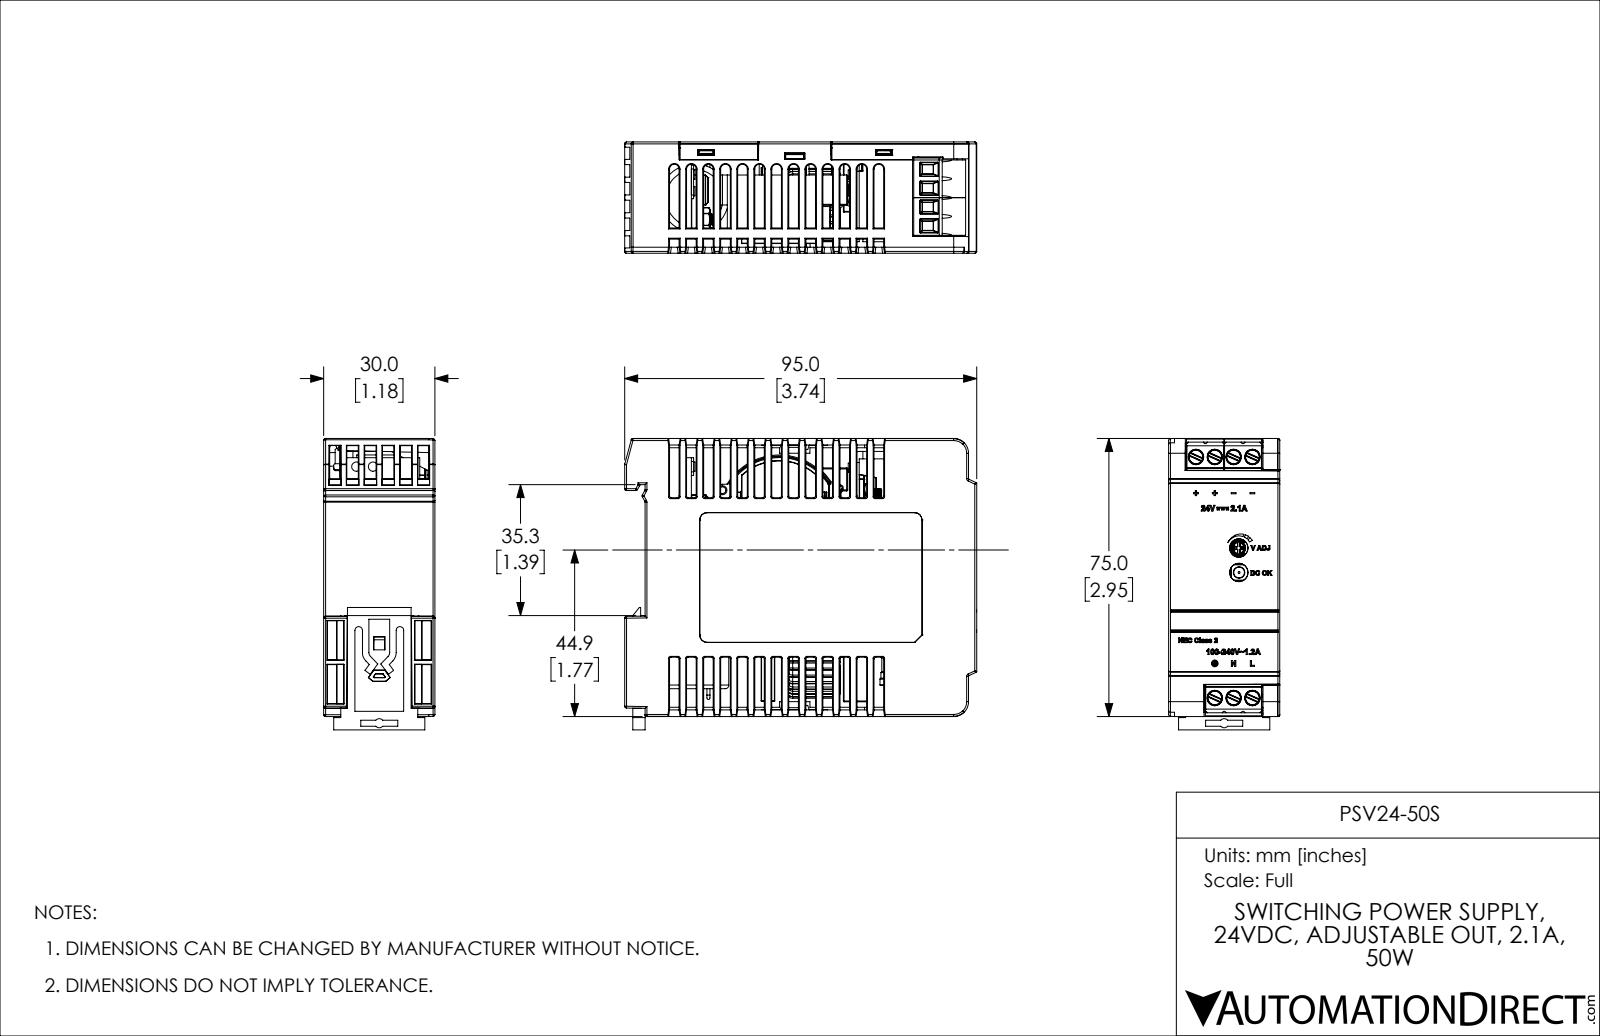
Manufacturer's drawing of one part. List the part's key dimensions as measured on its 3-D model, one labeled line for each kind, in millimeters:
Part name (STEP PRODUCT): PSV24-50S
STEP written by: SolidWorks 2017 (AUTOMOTIVE_DESIGN)
Units: millimetres
Bodies: 7 solids, 4339 faces (2175 planar, 1073 cylindrical, 1091 other)
Overall size (bounding box): 95 × 78.6 × 30
Volume: 48 980 mm³ · Surface area: 68 060 mm²
Round holes (diameter × count): ⌀4 ×7, ⌀4 ×7, ⌀3.5 ×1
Round bosses / shafts (diameter × count): ⌀3.9 ×7, ⌀3.4 ×1, ⌀2.9 ×1
Partial cylindrical surfaces — rounded edges, fillets, slot ends (radius × count): R0.1 ×656, R0.5 ×111, R0.3 ×16, R0.5 ×9, R0.2 ×8, R1.2 ×7, R1.5 ×5, R0.1 ×4
Main face-to-face distances: 1.6, 4.3, 28.4, 24.1, 5.9, 2.7, 26.8, 22.5, 1.4, 30
Hole centre spacings: 5.1, 65.2, 10.2, 65, 65.8, 15.2, 24.6, 24.8
